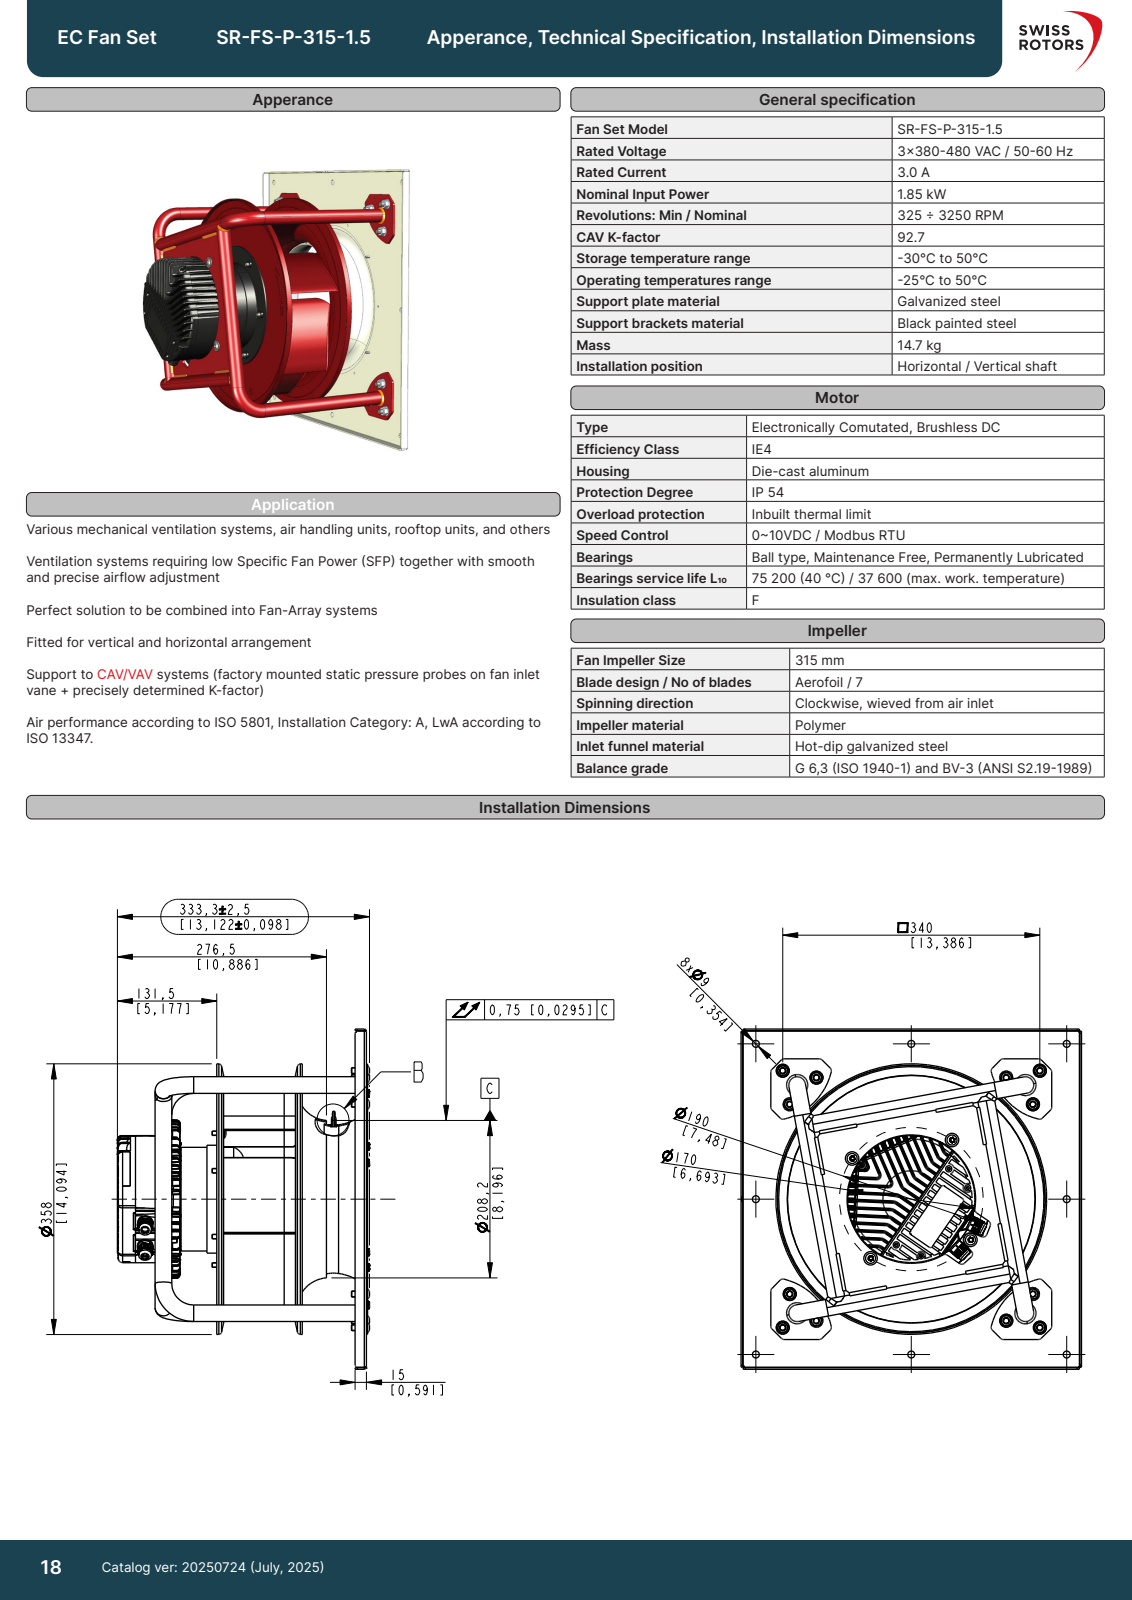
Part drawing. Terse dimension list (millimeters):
name: 1200110_12321
written by: CREO PARAMETRIC BY PTC INC, 2022014 (CONFIG_CONTROL_DESIGN)
unit: mm
bodies: 3 solids, 6290 faces (1799 planar, 2277 cylindrical, 2214 other)
size: 450 × 450 × 327.8
volume: 9 437 000 mm³; area: 1 794 000 mm²
holes: 8× ⌀9, 8× ⌀10, 7× ⌀4.5, 6× ⌀3.6, 6× ⌀5, 6× ⌀6, 6× ⌀8.8, 6× ⌀9.89, 6× ⌀13, 6× ⌀14, 4× ⌀6.8, 4× ⌀8
bosses: 8× ⌀17.7, 6× ⌀11, 6× ⌀9, 6× ⌀6.4, 6× ⌀4, 5× ⌀4.9, 4× ⌀18, 4× ⌀8
rounds: 475× R1, 344× R0.6, 160× R1.5, 144× R8.52, 124× R0.5, 108× R4.24, 108× R6.23, 48× R0.68
face distances: 2, 192.9, 190.9, 4, 188.9, 186.9, 268.4, 266.4, 79.5, 75.5
hole spacings: 205.5, 140, 87.5, 163.02, 166.21, 226.4, 233.32, 290.62
